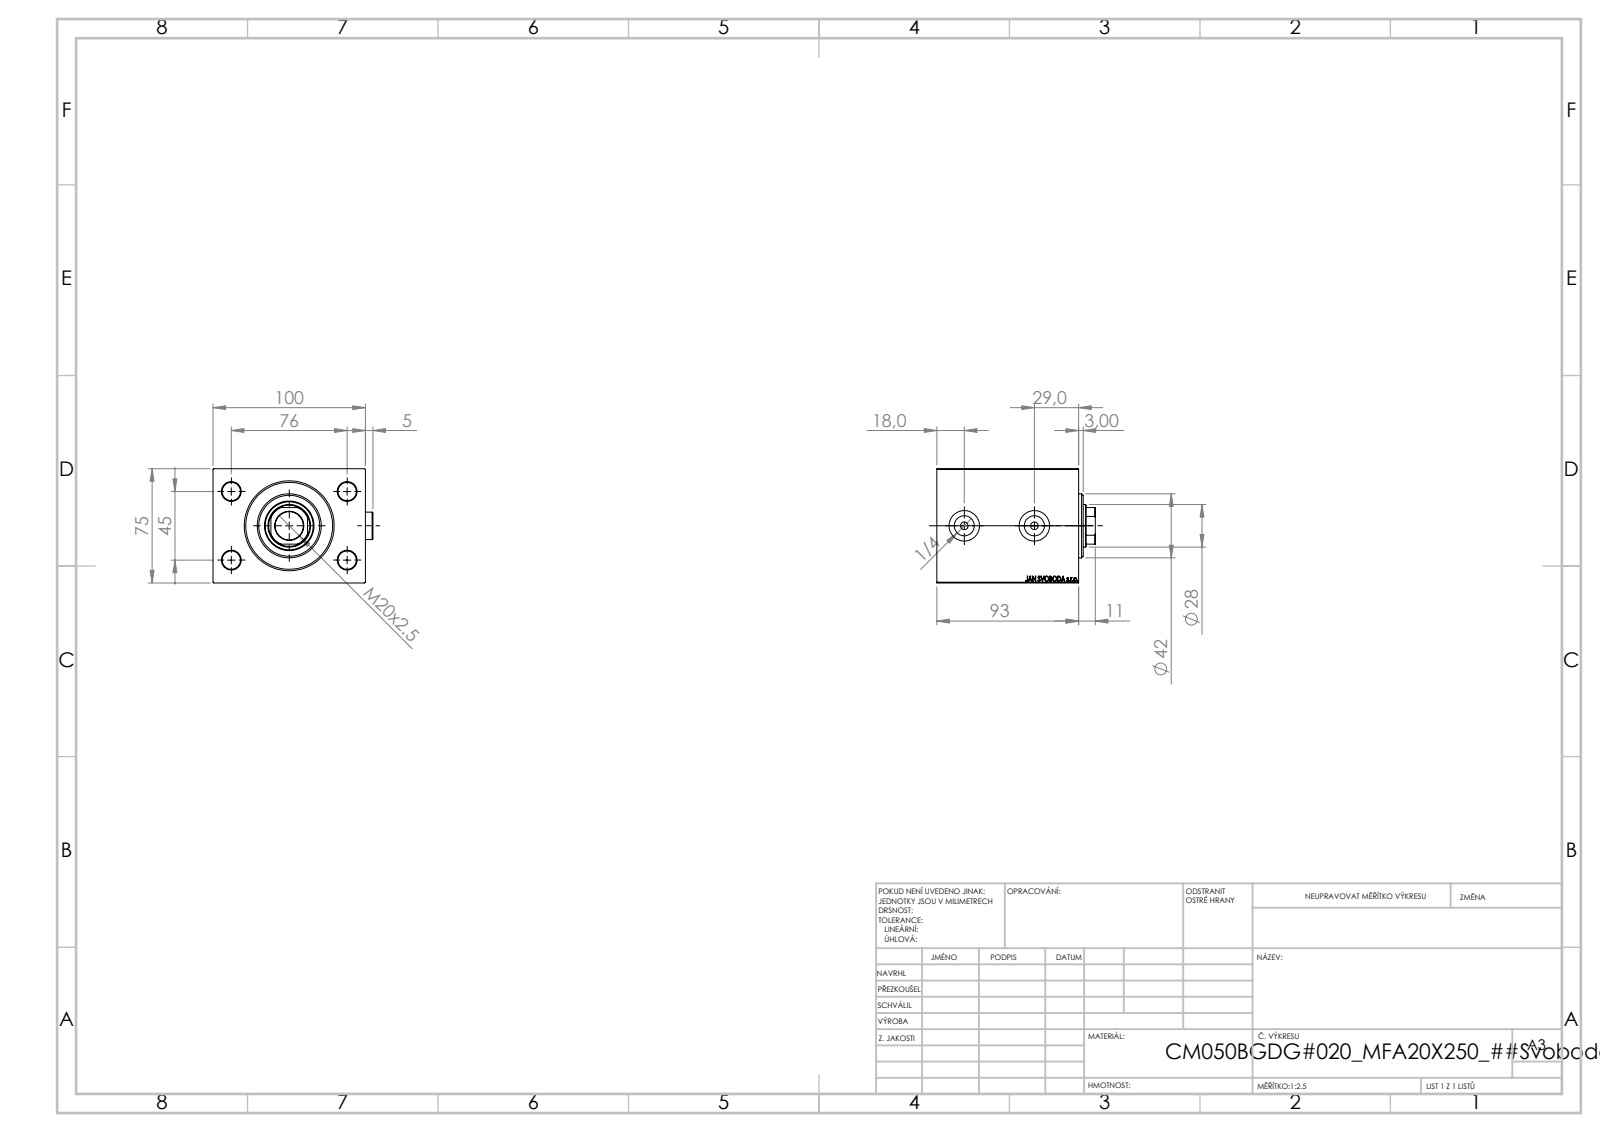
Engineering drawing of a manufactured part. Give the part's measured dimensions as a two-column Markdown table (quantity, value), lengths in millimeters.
| quantity | value |
| --- | --- |
| part name | V450CM_VC_B; V450CM_B_VCP; V450CM_B_Body; Zatka_OIL_PORT |
| STEP written by | SolidWorks 2019 (CONFIG_CONTROL_DESIGN) |
| units | millimeters |
| bodies | 5 solids, 936 faces (436 planar, 70 cylindrical, 430 other) |
| overall size | 104.9 × 104 × 75 |
| volume | 658 804 mm³ |
| surface area | 89 193 mm² |
| round holes (diameter × count) | 12 × 4, 5 × 2, 13.16 × 2, 20 × 2, 18.5 × 1, 28 × 1, 31.5 × 1, 32.5 × 1, 50 × 1, 52 × 1, 57 × 1 |
| round bosses / shafts (diameter × count) | 18 × 2, 42 × 1 |
| partial cylindrical surfaces (radius × count) | 13.5 × 1 |
| main face-to-face distances | 75, 100, 93, 42, 51, 21.6, 29.4, 71.4, 10, 31.6 |
| hole center spacings | 44.16, 45, 76, 88.32, 46 |
